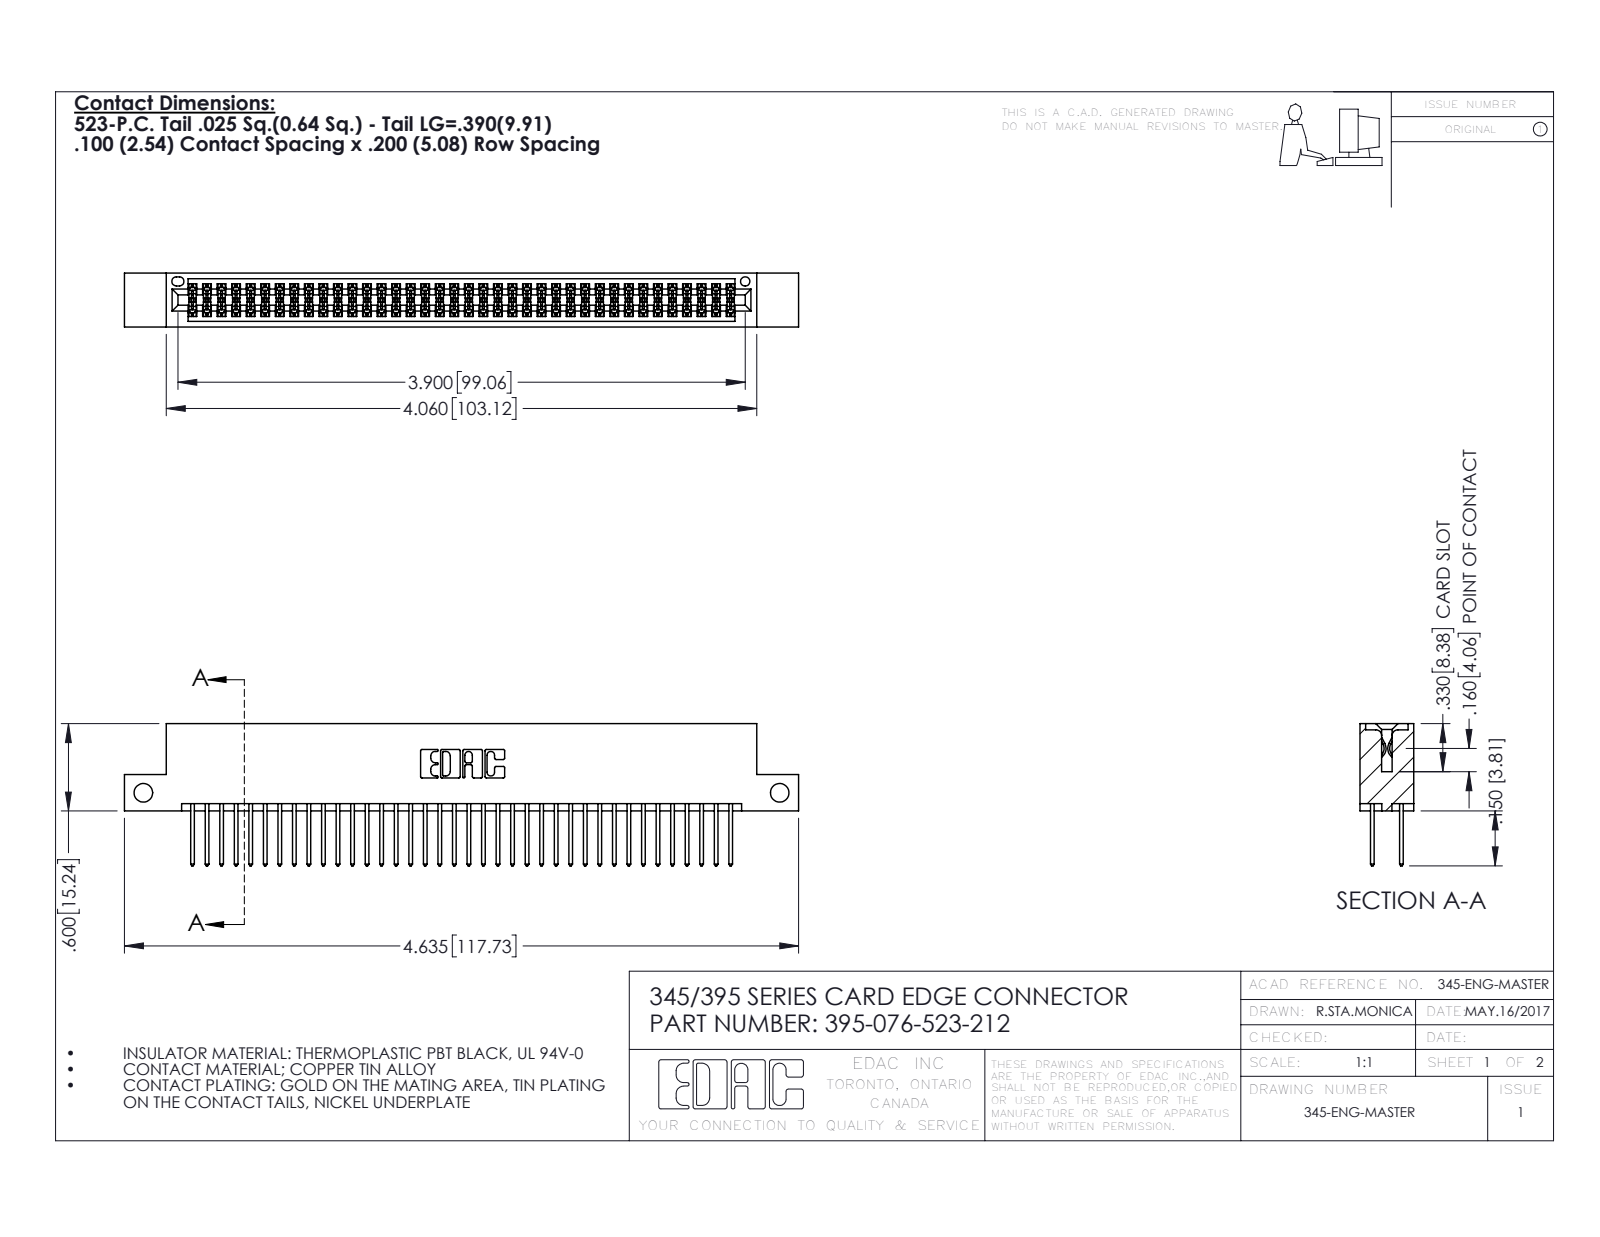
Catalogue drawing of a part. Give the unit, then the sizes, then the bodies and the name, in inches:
Units: inches
Overall size (bounding box): 4.635 × 0.977 × 0.37
Round holes (diameter × count): ⌀0.128 ×2, ⌀0.064 ×1
Partial cylindrical surfaces — rounded edges, fillets, slot ends (radius × count): R0.006 ×114, R0.01 ×76, R0.01 ×22, R0.007 ×6, R0.031 ×6, R0.026 ×3, R0.014 ×2, R0.019 ×2
Main face-to-face distances: 0.298, 0.072, 0.2, 0.098, 0.272, 0.025, 0.37, 0.225, 0.175, 0.149
Hole centre spacings: 4.375
Volume: 0.7 in³ · Surface area: 27.03 in²
Bodies: 77 solids, 3926 faces (2588 planar, 1338 cylindrical, 0 other)
Part name (STEP PRODUCT): 345-292-001_345-293-123; 345 Part_Flush Mounting Lugs - Side Mount; 395-076-523-212
STEP written by: SolidWorks 2016 (CONFIG_CONTROL_DESIGN)
